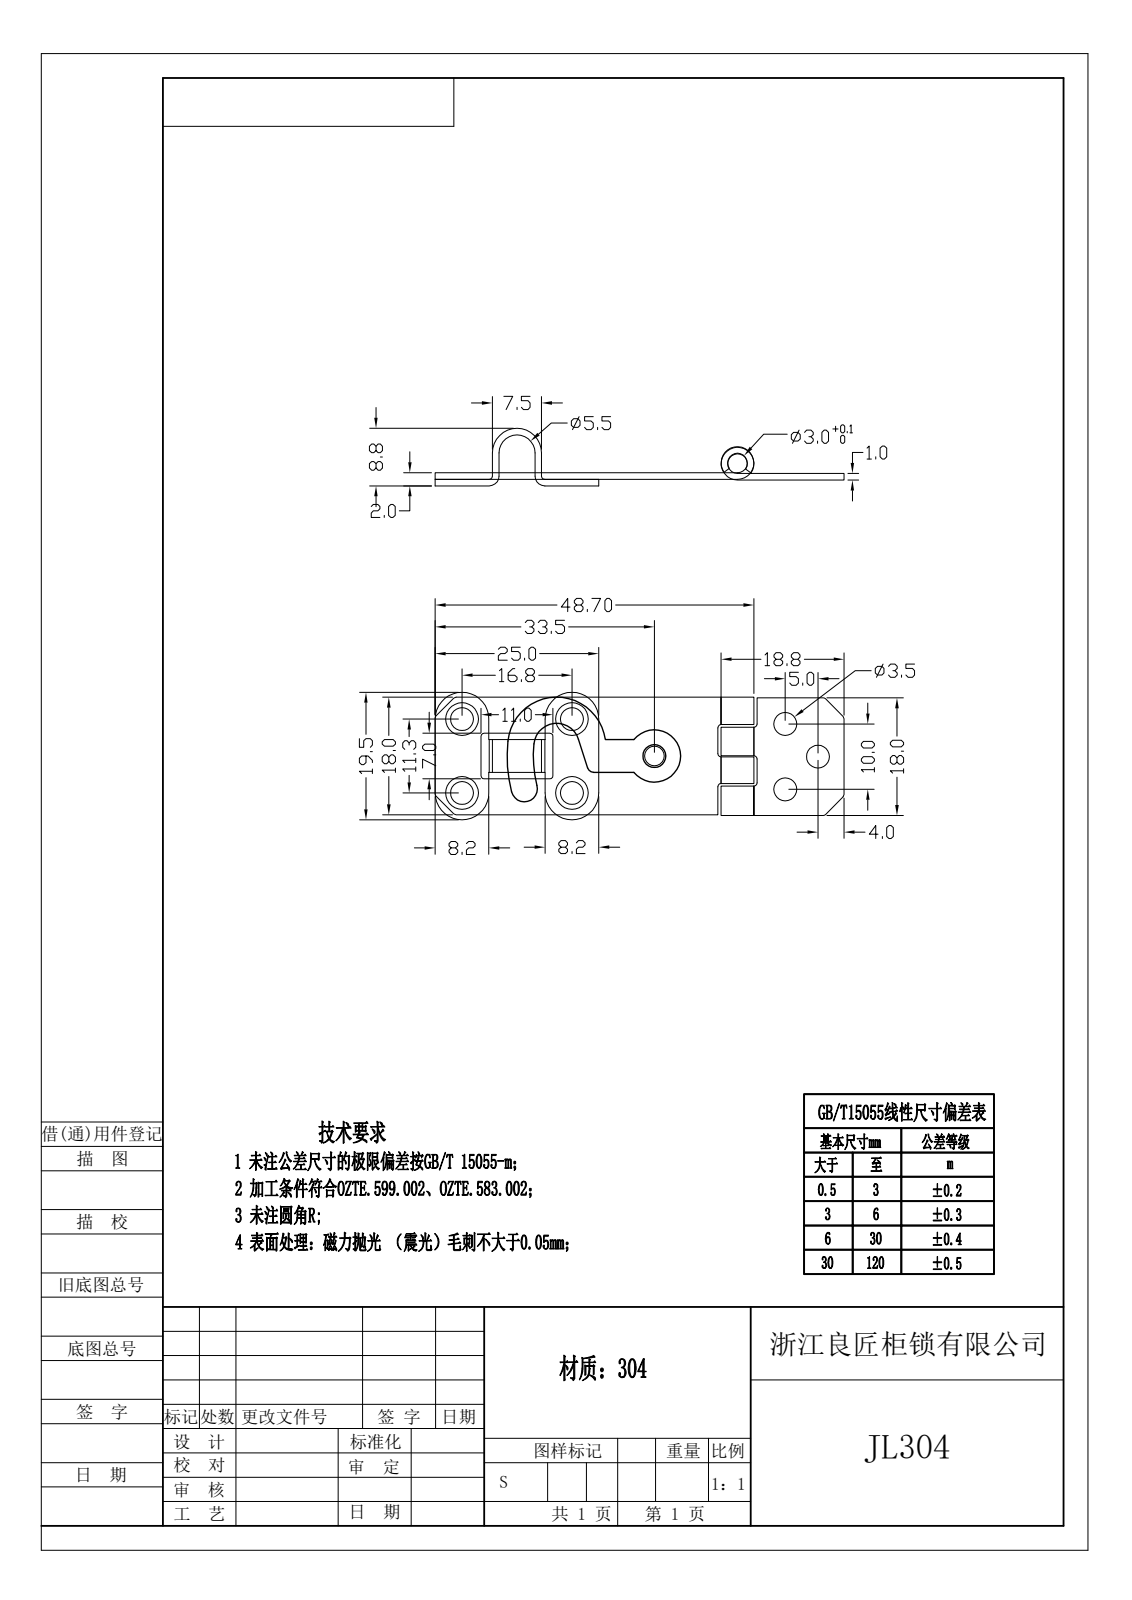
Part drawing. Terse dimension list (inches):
written by: Rhino 8.5 (CONFIG_CONTROL_DESIGN)
unit: in
bodies: 5 solids, 140 faces (72 planar, 58 cylindrical, 10 other)
size: 2.461 × 0.768 × 0.335
volume: 0.101 in³; area: 6.143 in²
holes: 4× ⌀0.138, 1× ⌀0.118
bosses: 2× ⌀0.197
rounds: 21× R0.02, 4× R0.161, 2× R0.059, 1× R0.039, 1× R0.079, 1× R0.108, 1× R0.138, 1× R0.148
face distances: 0.039, 0.079, 0.118, 0.157, 0.256, 0.709, 0.453, 0.276, 0.183, 0.171
hole spacings: 0.278, 0.812, 0.394, 0.984
